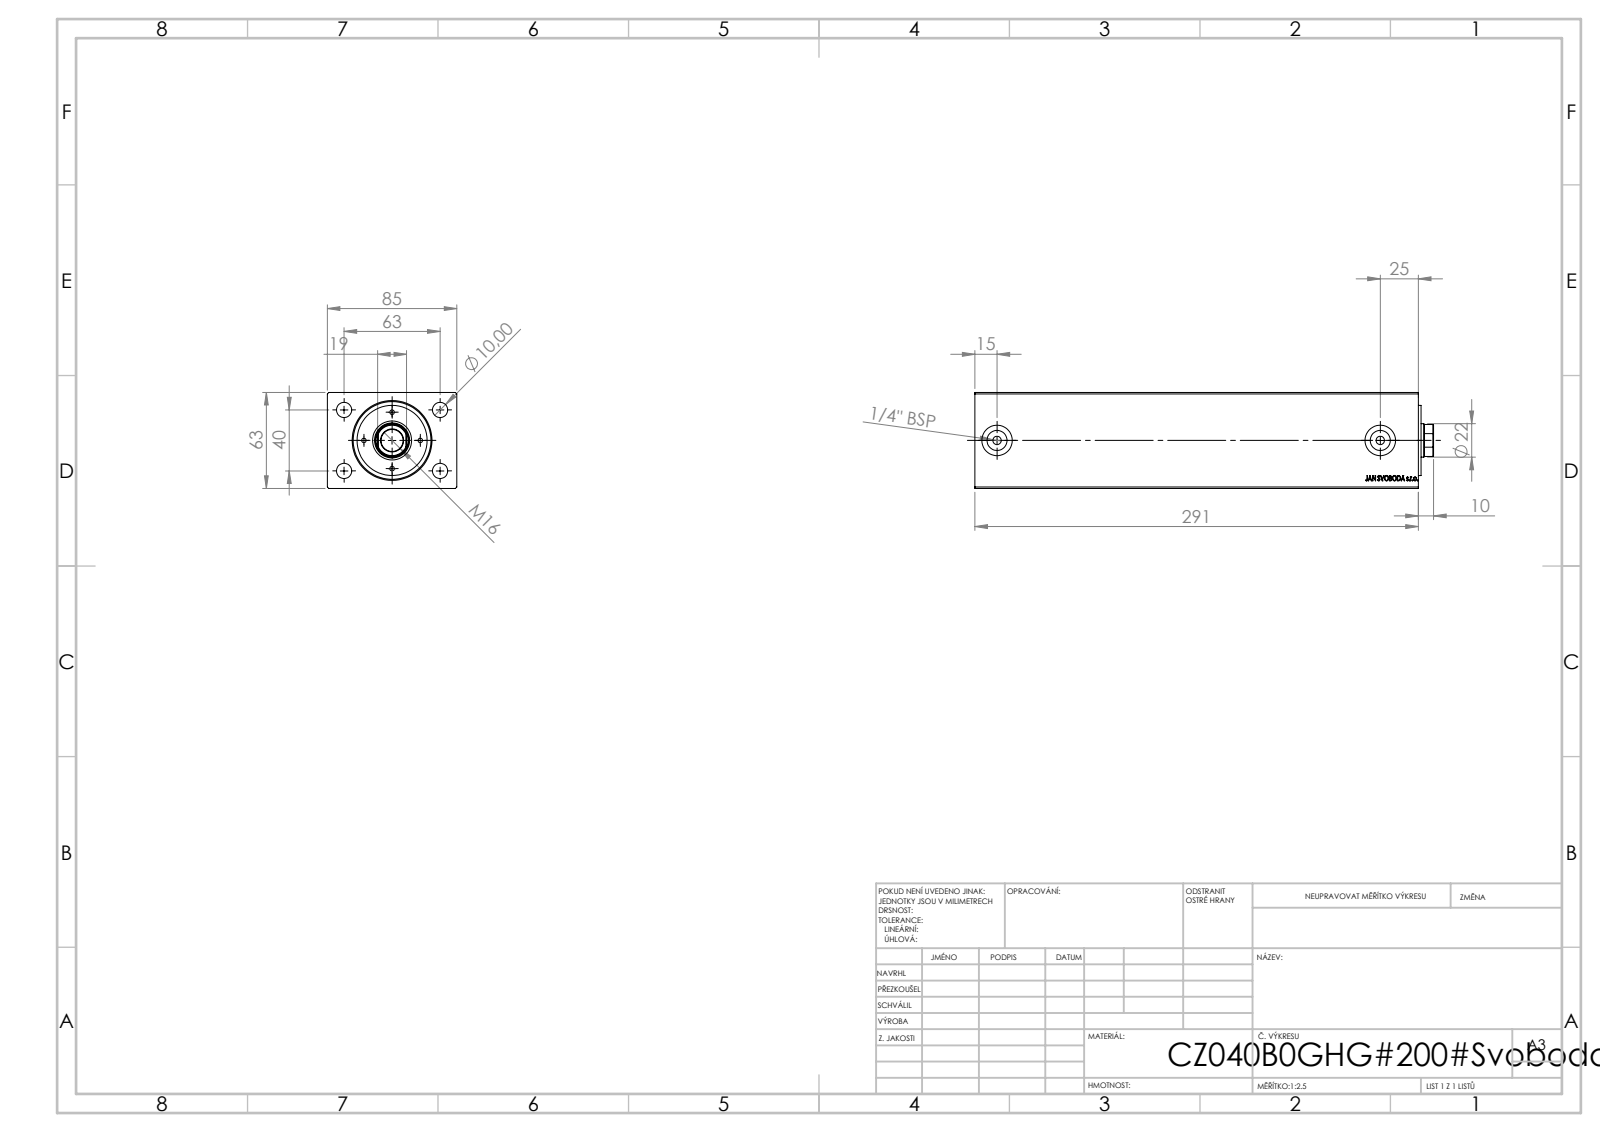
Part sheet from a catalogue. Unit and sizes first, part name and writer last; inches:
Units: inches
Overall size (bounding box): 11.85 × 3.346 × 2.48
Round holes (diameter × count): ⌀0.118 ×4, ⌀0.394 ×4, ⌀0.217 ×2, ⌀0.518 ×2, ⌀0.787 ×2, ⌀0.571 ×1, ⌀0.866 ×1, ⌀0.906 ×1, ⌀1.417 ×1, ⌀1.575 ×1, ⌀2.008 ×1
Round bosses / shafts (diameter × count): ⌀1.811 ×1
Partial cylindrical surfaces — rounded edges, fillets, slot ends (radius × count): R0.413 ×1
Main face-to-face distances: 2.48, 3.346, 11.457, 10.854, 0.602, 0.394, 0.071, 0.323, 10.531, 11.134
Hole centre spacings: 0.728, 0.939, 1.03, 1.242, 1.469, 1.958, 2.12, 1.457
Volume: 82.99 in³ · Surface area: 265.7 in²
Bodies: 3 solids, 874 faces (400 planar, 58 cylindrical, 416 other)
Part name (STEP PRODUCT): V500CZ; V500CZ_B_VC
STEP written by: SolidWorks 2019 (CONFIG_CONTROL_DESIGN)
